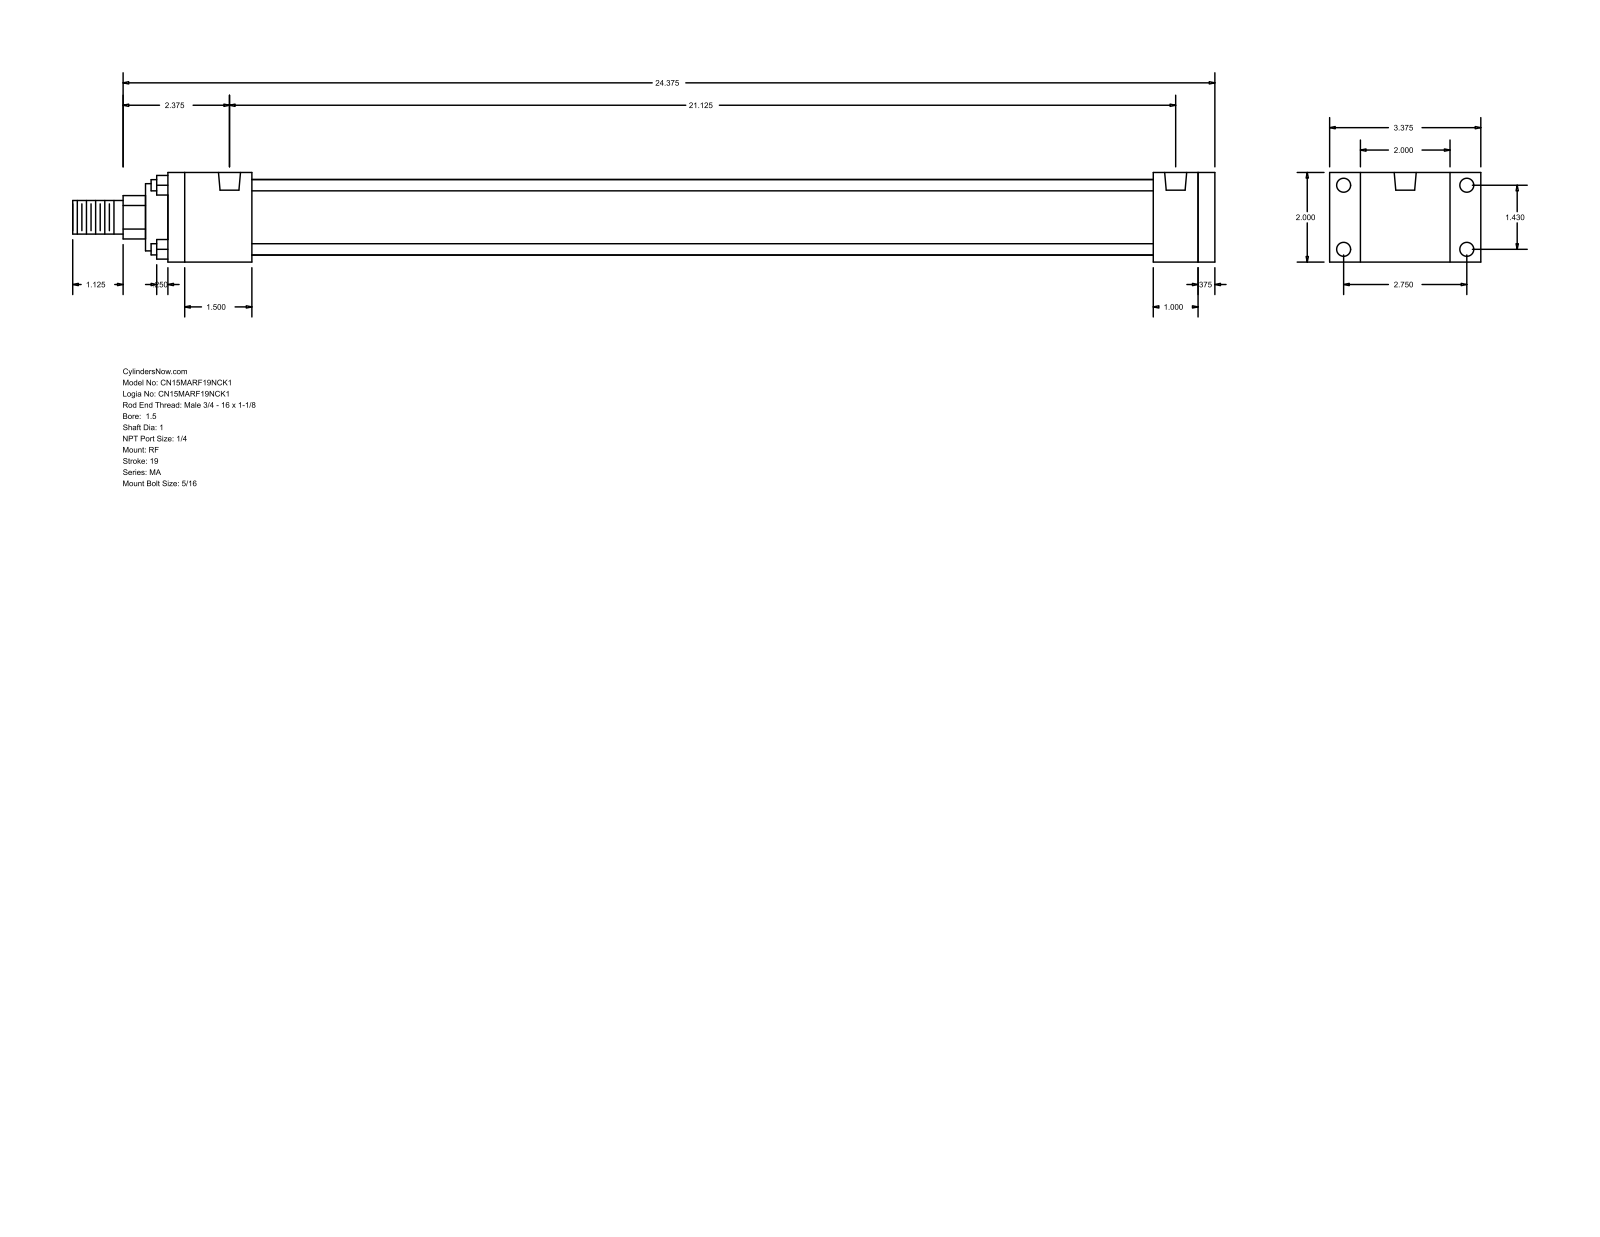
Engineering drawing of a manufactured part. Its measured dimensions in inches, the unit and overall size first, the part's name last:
Units: inches
Overall size (bounding box): 25.5 × 3.375 × 2
Round holes (diameter × count): ⌀0.313 ×8, ⌀0.492 ×2
Round bosses / shafts (diameter × count): ⌀0.25 ×4, ⌀1.69 ×1, ⌀1.5 ×1, ⌀1 ×1, ⌀0.75 ×1
Partial cylindrical surfaces — rounded edges, fillets, slot ends (radius × count): R0.484 ×1
Main face-to-face distances: 2, 0.375, 23.375, 23, 1, 22, 1.375, 1.875, 20.125, 21.125
Hole centre spacings: 1.43, 2.75, 3.099, 21.125
Bodies: 0 solids, 92 faces (64 planar, 28 cylindrical, 0 other)
Part name (STEP PRODUCT): MA_RF__0150_1
STEP written by: GSSL Pune (CONFIG_CONTROL_DESIGN)
